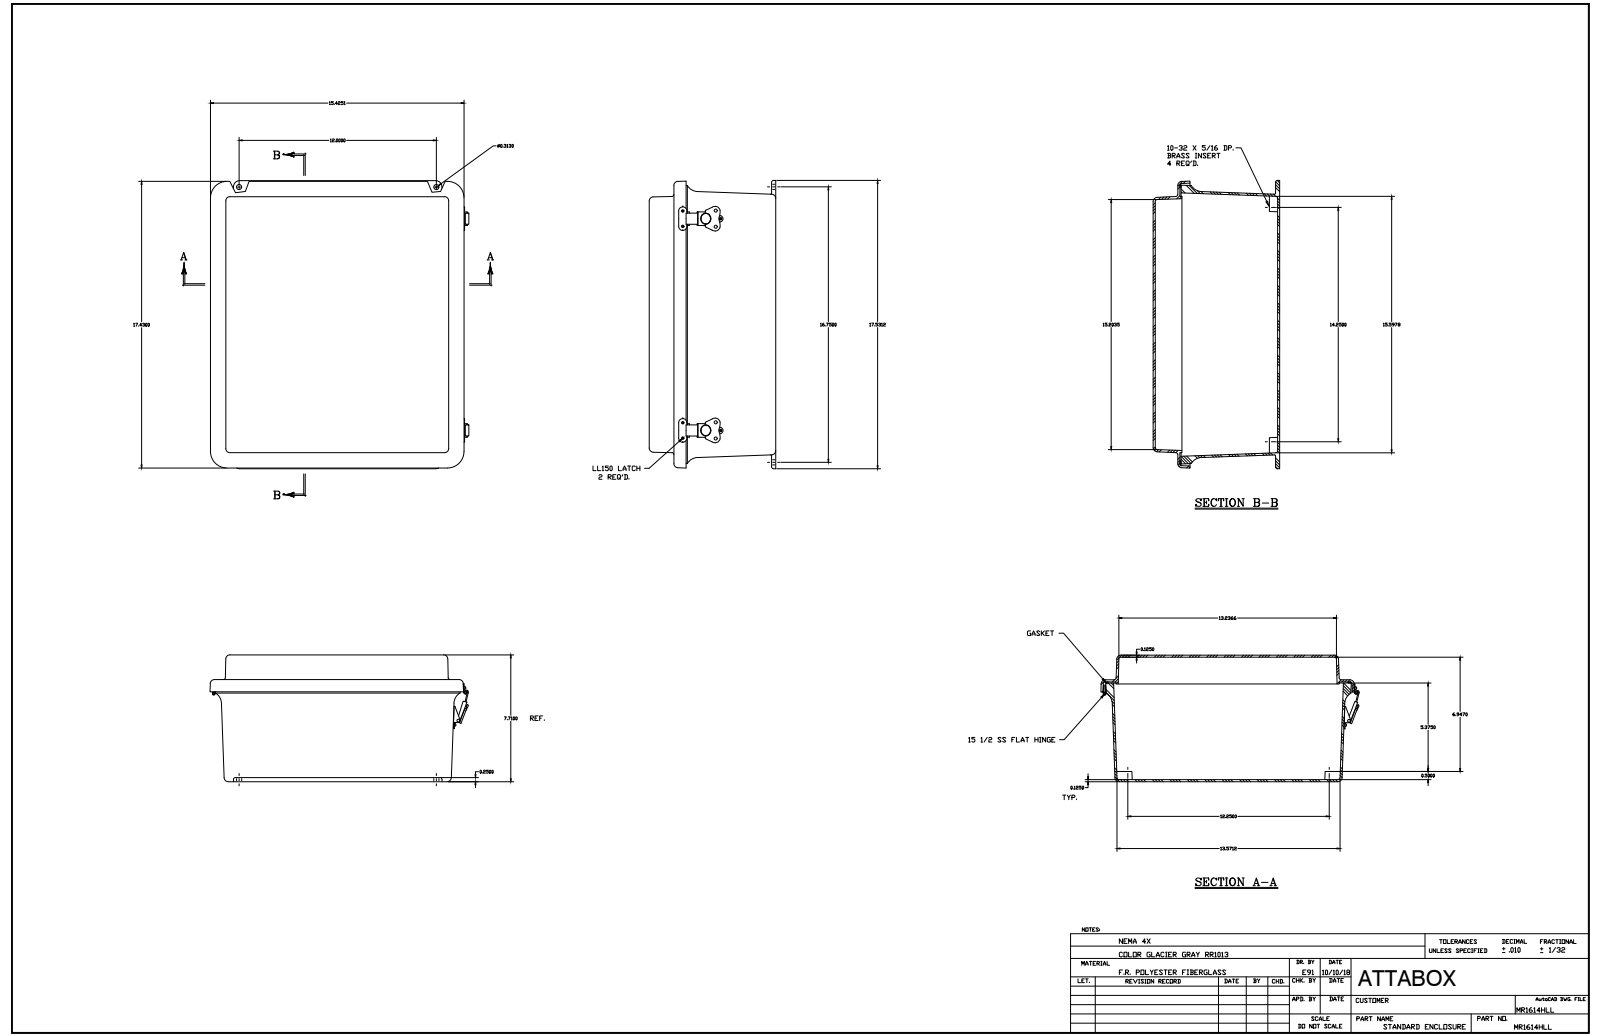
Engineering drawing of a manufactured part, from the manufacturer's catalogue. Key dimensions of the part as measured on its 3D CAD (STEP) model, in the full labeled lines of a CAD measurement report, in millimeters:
Part name (STEP PRODUCT): MR1614HLL
STEP written by: SolidWorks 2018 (AUTOMOTIVE_DESIGN)
Units: millimetres
Bodies: 50 solids, 1315 faces (590 planar, 508 cylindrical, 217 other)
Overall size (bounding box): 445.3 × 396.9 × 195.5
Volume: 2 415 000 mm³ · Surface area: 1 375 000 mm²
Round holes (diameter × count): ⌀3.6 ×18, ⌀3.3 ×10, ⌀3.9 ×8, ⌀3.3 ×4, ⌀4 ×4, ⌀4.2 ×4, ⌀5 ×4, ⌀5.5 ×4, ⌀3 ×2, ⌀3.5 ×2, ⌀4.6 ×2, ⌀4.6 ×2
Round bosses / shafts (diameter × count): ⌀6.4 ×18, ⌀3.2 ×9, ⌀3.2 ×9, ⌀6.9 ×4, ⌀14.8 ×2, ⌀13.3 ×2, ⌀5.3 ×2, ⌀4.7 ×2
Partial cylindrical surfaces — rounded edges, fillets, slot ends (radius × count): R0.8 ×20, R2 ×20, R3.2 ×20, R6.4 ×20, R0.9 ×8, R1 ×8, R1.1 ×8, R1.2 ×8
Main face-to-face distances: 3.2, 3.2, 189.2, 195.5, 192.3, 192.3, 38.2, 151, 154.2, 41.3
Hole centre spacings: 95.3, 190.5, 285.8, 326.8, 326.9, 6.4, 88.9, 23.8
